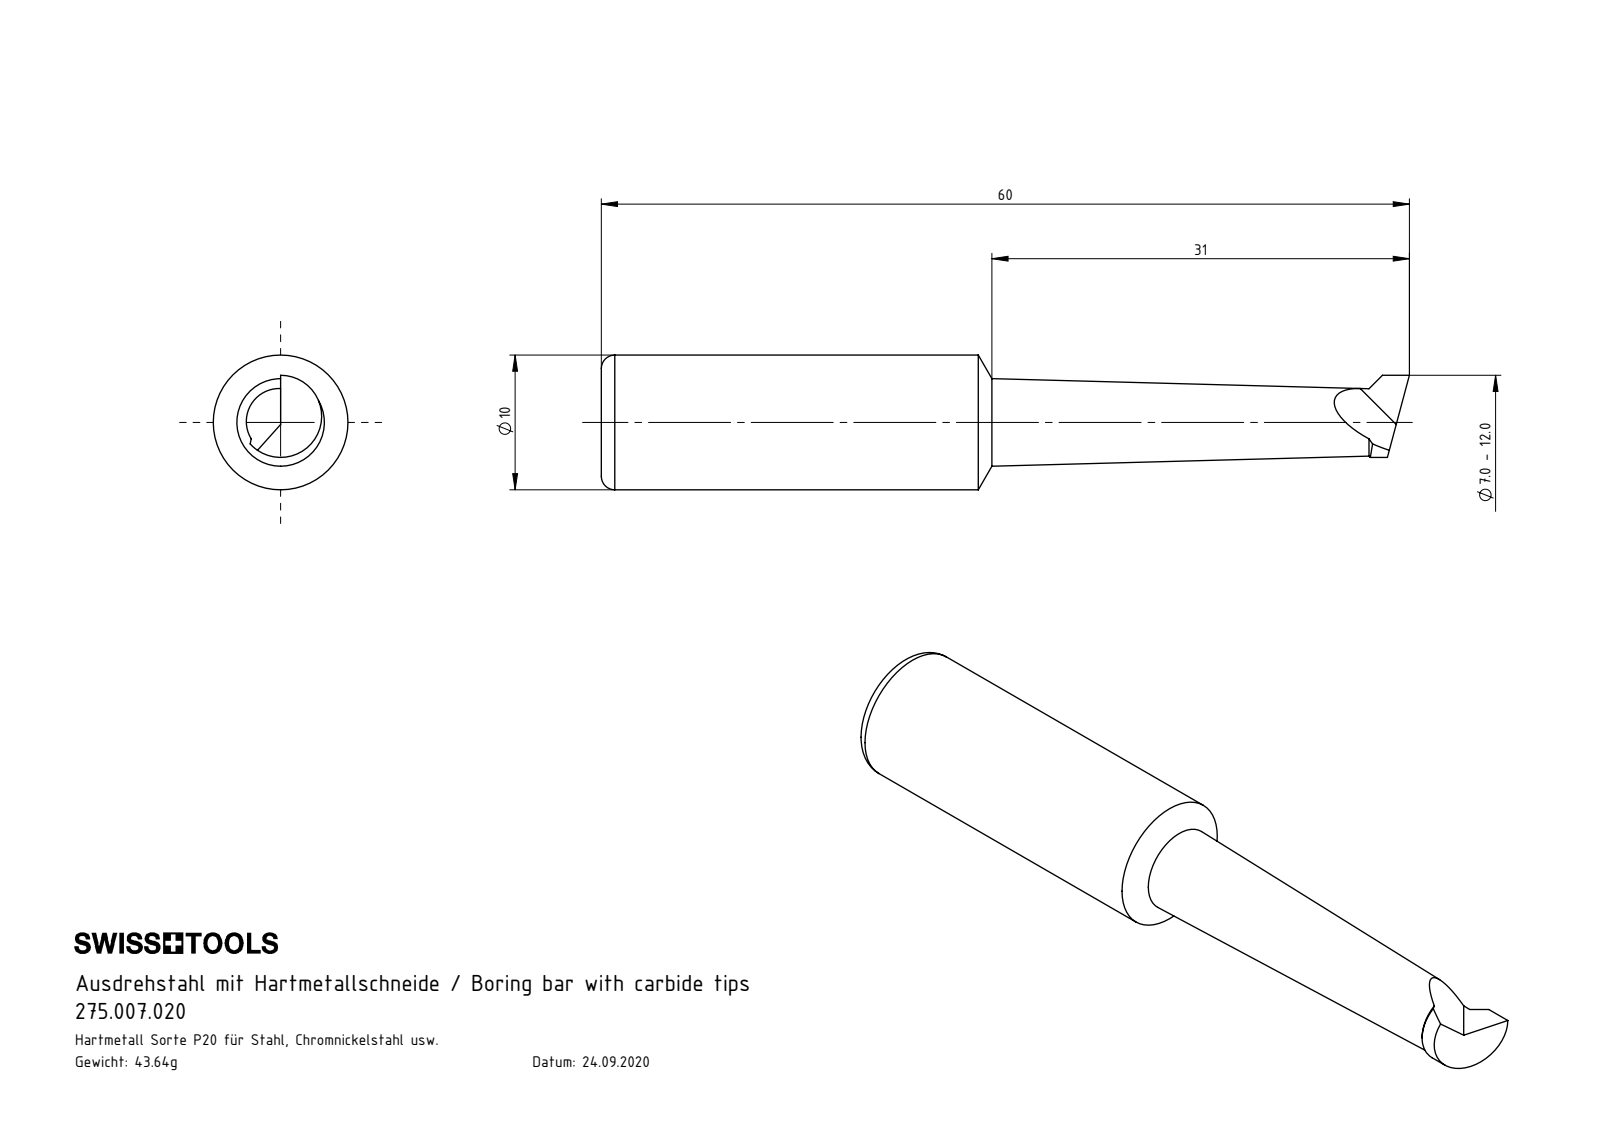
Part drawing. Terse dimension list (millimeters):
name: 275.007.020
written by: SolidWorks 2022 (AUTOMOTIVE_DESIGN)
unit: mm
bodies: 1 solid, 14 faces (4 planar, 3 cylindrical, 7 other)
size: 60 × 10 × 10
volume: 3 010 mm³; area: 1 559 mm²
bosses: 1× ⌀10
rounds: 1× R3.05
